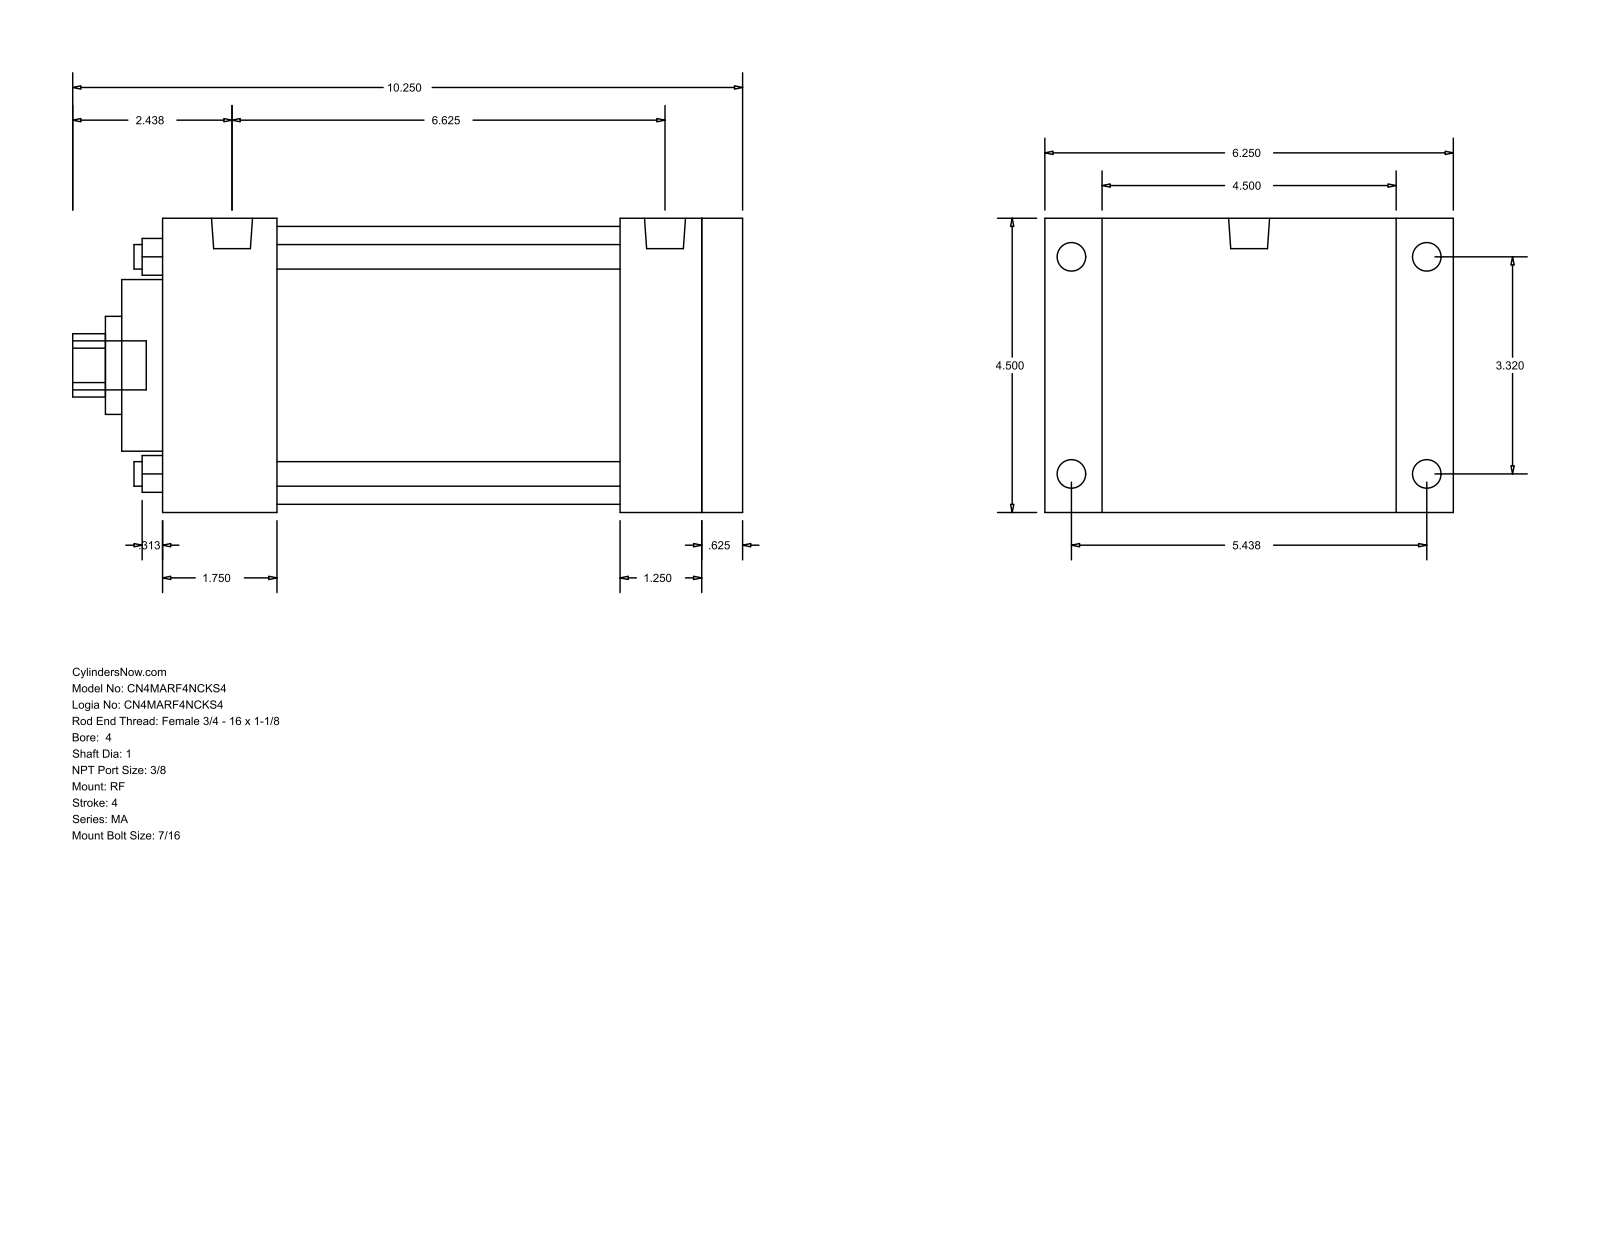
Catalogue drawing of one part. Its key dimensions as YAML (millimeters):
part_name: "MA_RF__0400_1"
step_written_by: "GSSL Pune (CONFIG_CONTROL_DESIGN)"
units: millimeters
bodies: {solids: 0, faces: 94, planar: 65, cylindrical: 29, other: 0}
overall_size: [260.35, 158.75, 114.3]
round_holes:
  - {diameter: 9.53, count: 4}
  - {diameter: 25.4, count: 1}
  - {diameter: 38.1, count: 1}
  - {diameter: 66.67, count: 1}
  - {diameter: 107.95, count: 1}
round_bosses_or_shafts:
  - {diameter: 11.11, count: 8}
  - {diameter: 15.93, count: 2}
  - {diameter: 19.05, count: 1}
partial_cylinders:
  - {radius: 12.29, count: 1}
face_to_face_distances: [114.3, 225.43, 209.55, 15.88, 22.23, 136.53, 177.8, 31.75, 47.63, 44.46]
hole_center_spacings: [59.62, 84.32, 119.25]
